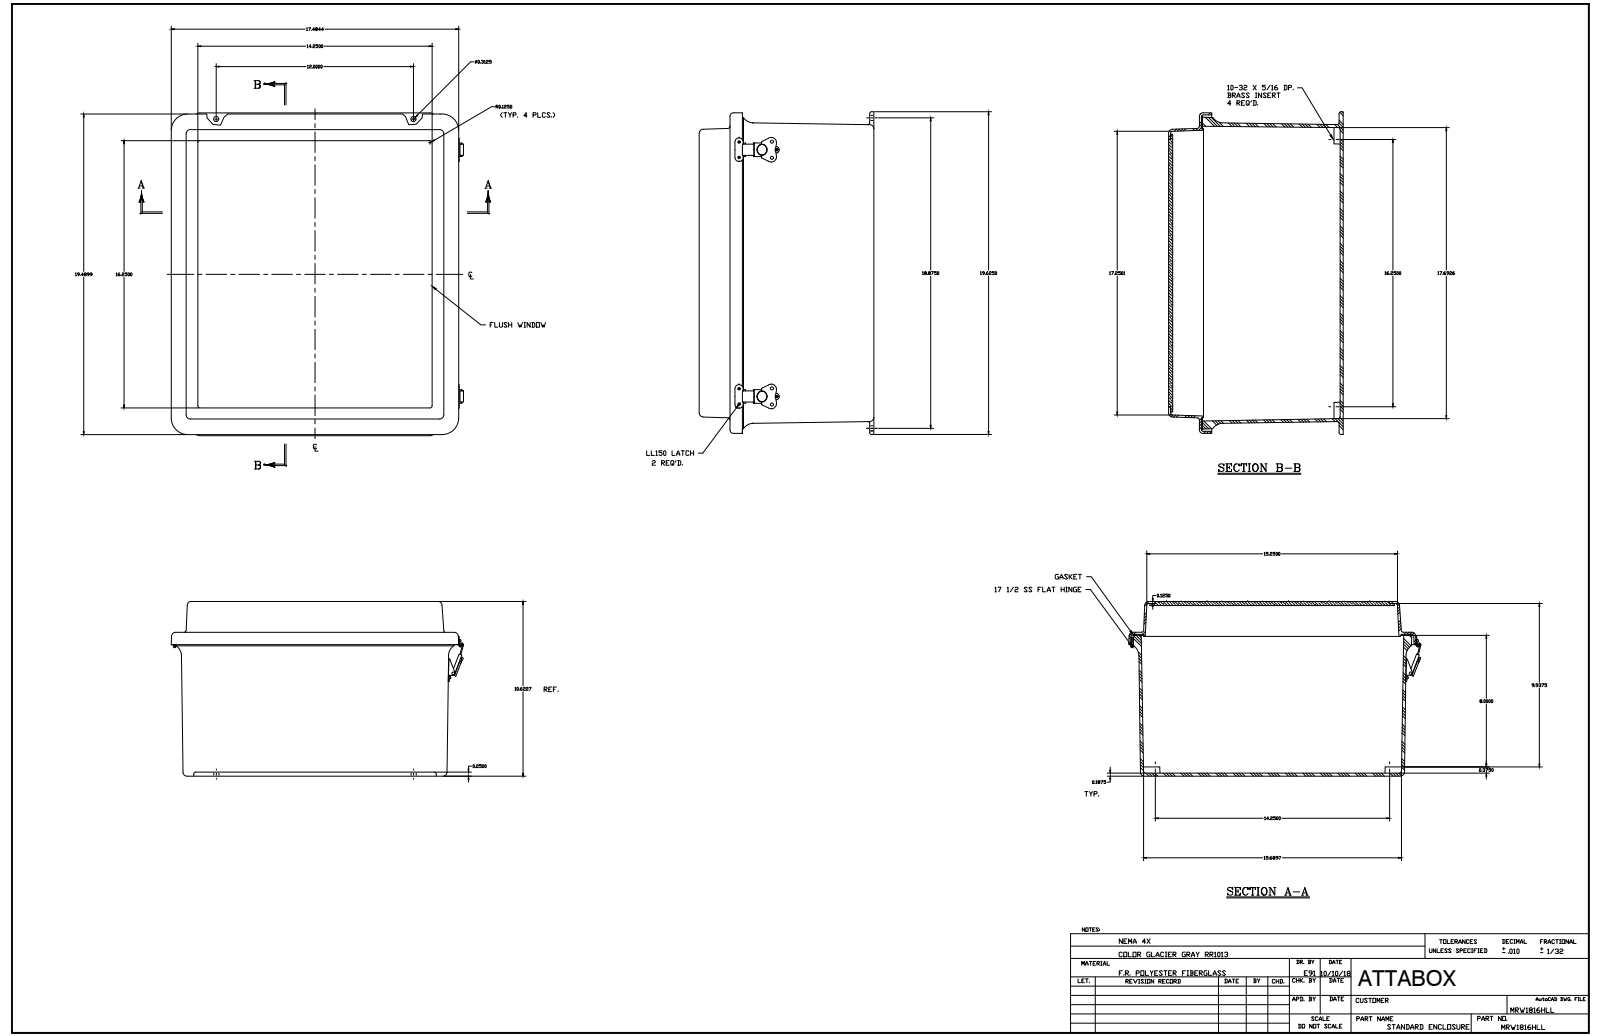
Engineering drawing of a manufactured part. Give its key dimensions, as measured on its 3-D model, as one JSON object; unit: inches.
{"part_name": "MRW1816HLL", "step_written_by": "SolidWorks 2018 (AUTOMOTIVE_DESIGN)", "units": "inches", "bodies": {"solids": 53, "faces": 1395, "planar": 631, "cylindrical": 541, "other": 223}, "overall_size": [19.625, 17.703, 10.642], "volume_in3": 281, "surface_area_in2": 3010, "round_holes": [[0.14, 20], [0.131, 12], [0.152, 5], [0.13, 4], [0.156, 4], [0.165, 4], [0.197, 4], [0.218, 4], [0.118, 2], [0.138, 2], [0.181, 2], [0.182, 2]], "round_bosses_or_shafts": [[0.25, 20], [0.125, 11], [0.125, 9], [0.27, 4], [0.583, 2], [0.524, 2], [0.209, 2], [0.185, 2]], "partial_cylinders_radius": [[0.125, 24], [0.031, 20], [0.079, 19], [0.25, 16], [0.037, 8], [0.039, 8], [0.045, 8], [0.047, 8]], "face_to_face_distances": [0.187, 0.25, 10.392, 0.188, 10.642, 10.454, 10.204, 0.125, 1.75, 2], "hole_center_spacings": [3.375, 3.375, 6.75, 14.984, 10.25, 14.984, 0.25, 9.75]}
